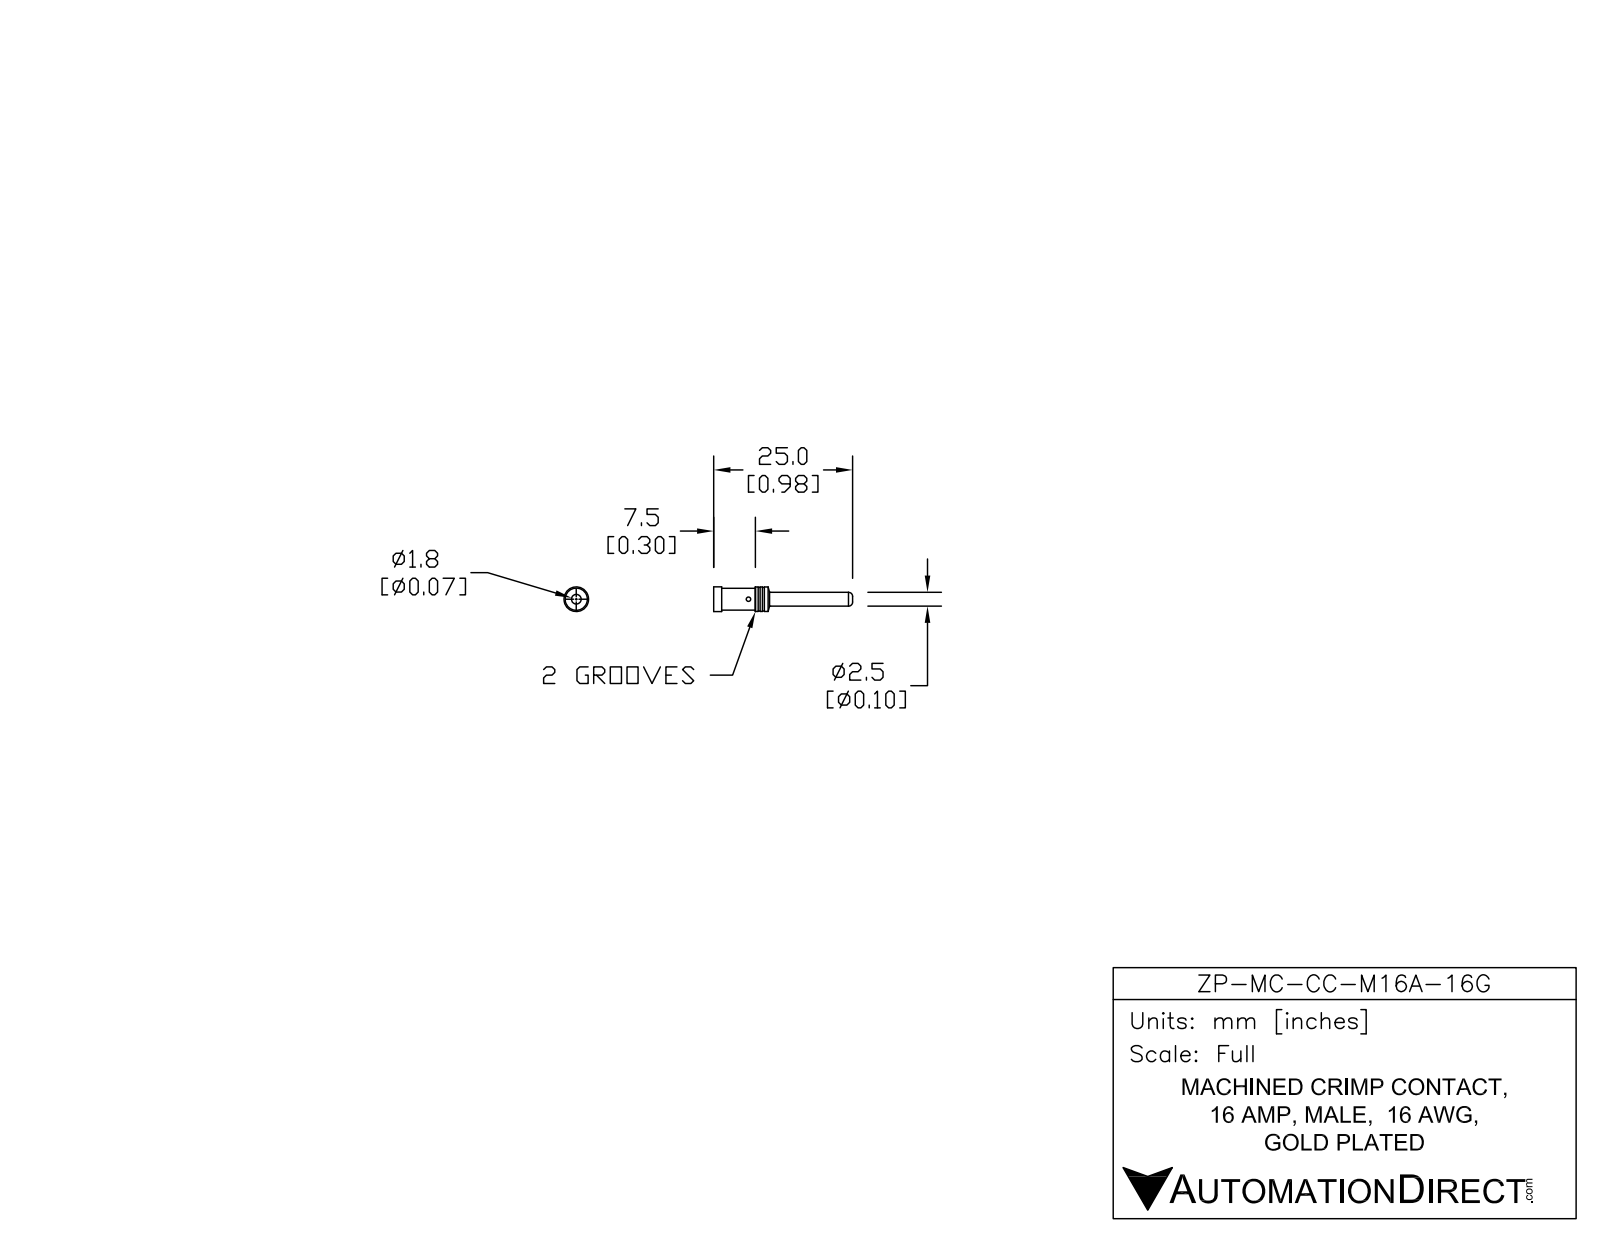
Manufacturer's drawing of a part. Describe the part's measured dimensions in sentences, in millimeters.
The part is named "ZP-MC-CC-M16A-16G". Its 3-D file was written by "SolidWorks 2014 (AUTOMOTIVE_DESIGN)". It is 1 solid with 36 faces: 8 planar, 20 cylindrical and 8 other. Overall it measures 25 by 4.42 by 4.42 millimeters. Its volume is 150 cubic millimeters and its surface area 320 square millimeters. Round holes: 1 of diameter 0.8, 1 of diameter 1.75. Round bosses or shafts: 1 of diameter 4.42, 1 of diameter 4.22, 1 of diameter 3.03, 1 of diameter 2.5. The main face-to-face distances are 7.5, 0.5, 8, 1.11, 1.61, 9.11, 0.35, 0.76, 1.26, 8.76.
